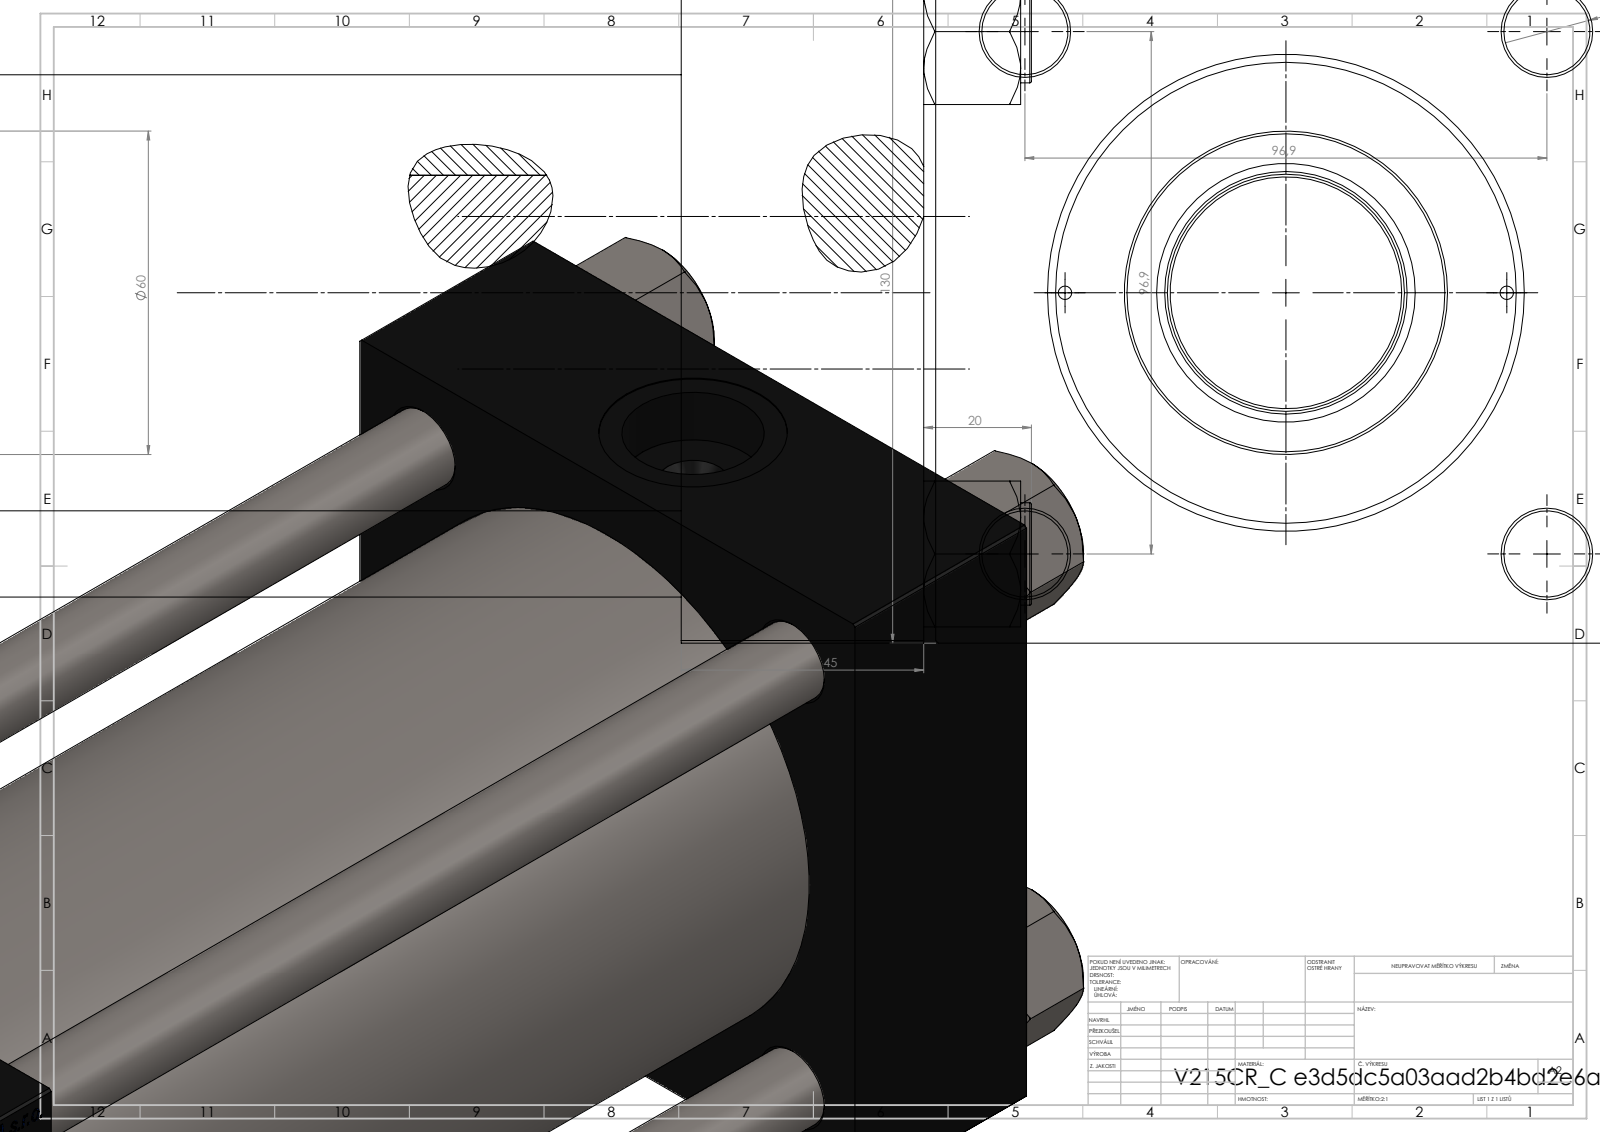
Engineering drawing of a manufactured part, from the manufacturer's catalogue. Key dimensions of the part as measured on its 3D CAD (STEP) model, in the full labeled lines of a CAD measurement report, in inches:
Part name (STEP PRODUCT): V215CR_C_TYCINKA; V215CR_C_Body; V215_VC_A; V215CR_ROD_END_F (+2 more)
STEP written by: SolidWorks 2019 (CONFIG_CONTROL_DESIGN)
Units: inches
Bodies: 12 solids, 1216 faces (579 planar, 95 cylindrical, 542 other)
Overall size (bounding box): 16.811 × 5.118 × 5.118
Volume: 179.9 in³ · Surface area: 733.8 in²
Round holes (diameter × count): ⌀0.63 ×4, ⌀0.098 ×2, ⌀0.276 ×2, ⌀1.041 ×2, ⌀1.378 ×2, ⌀1.24 ×1, ⌀1.772 ×1, ⌀1.89 ×1, ⌀2.992 ×1, ⌀3.366 ×1, ⌀3.937 ×1
Round bosses / shafts (diameter × count): ⌀0.748 ×4, ⌀4.173 ×1, ⌀2.362 ×1, ⌀1.732 ×1, ⌀1.299 ×1
Main face-to-face distances: 5.118, 1.772, 12.913, 11.142, 10.079, 8.307, 2.835, 3.78, 2.008, 6.299
Hole centre spacings: 1.93, 2.698, 3.815, 4.005, 1.614, 5.395, 3.228, 10.177
